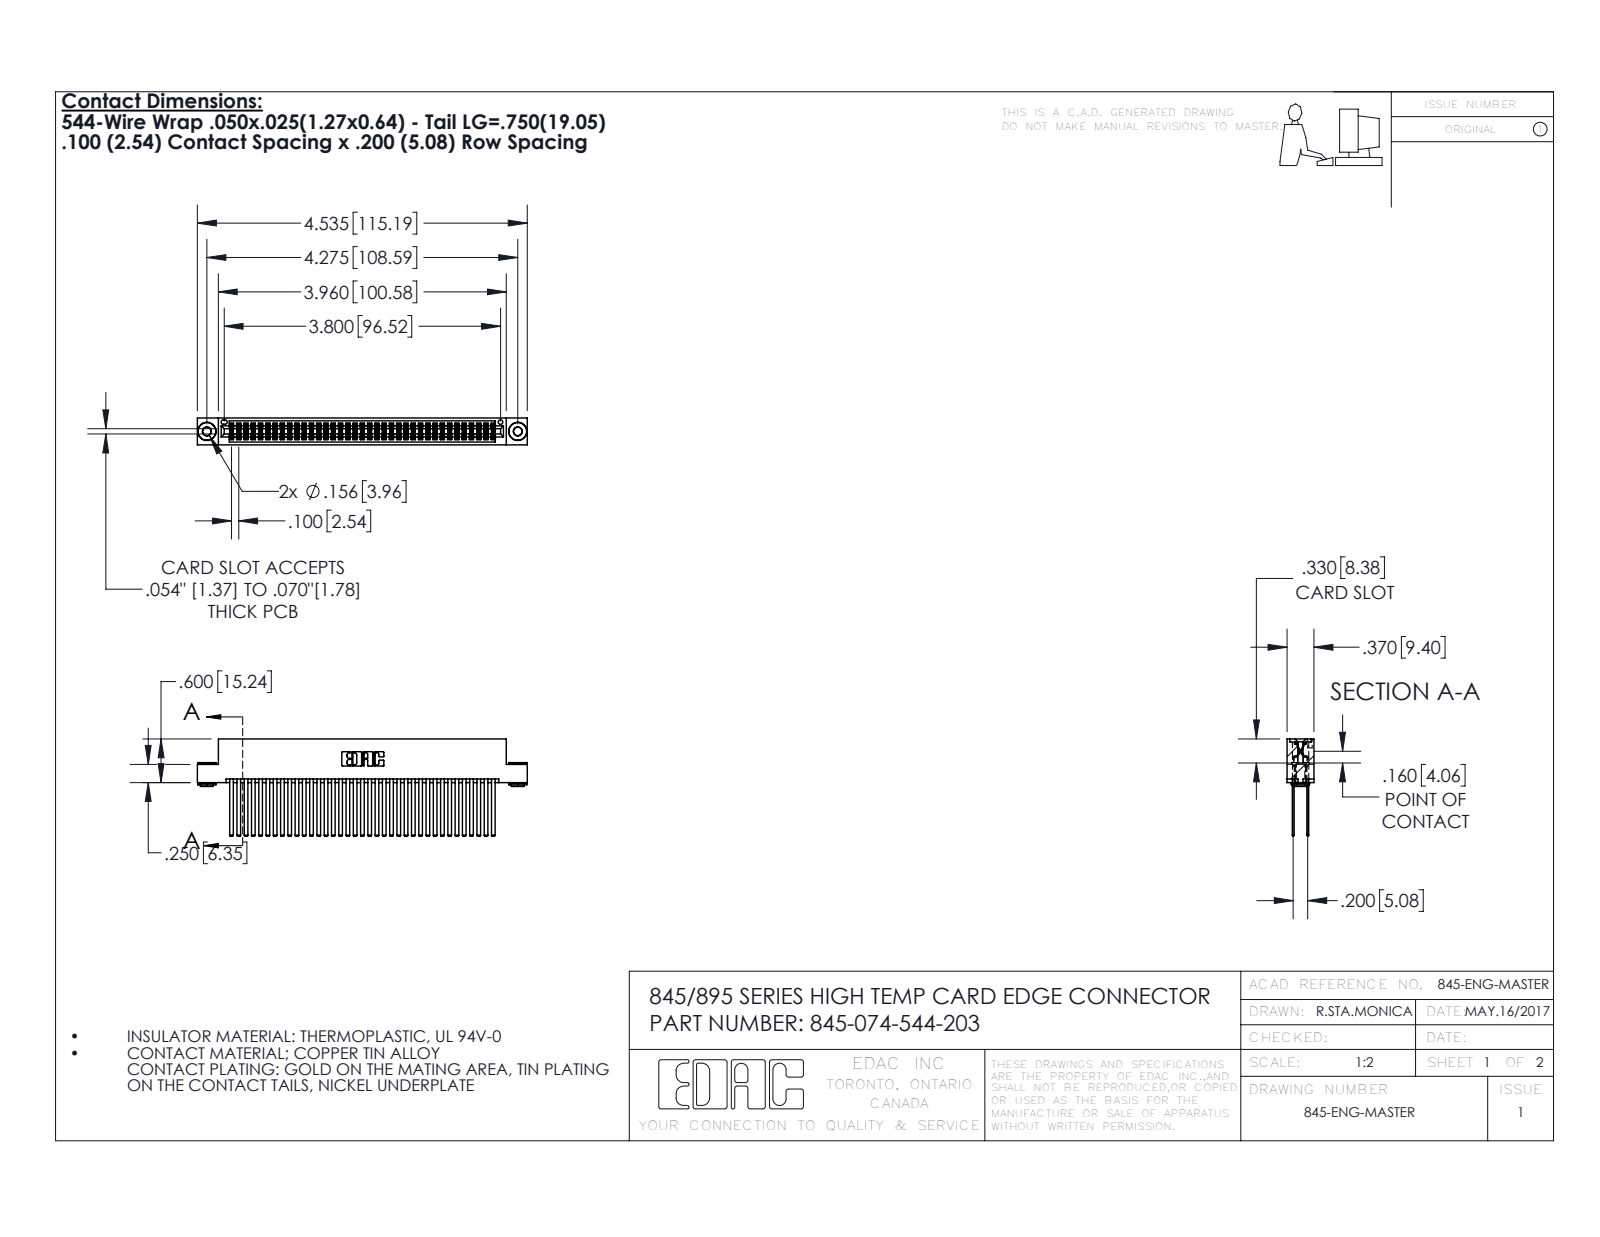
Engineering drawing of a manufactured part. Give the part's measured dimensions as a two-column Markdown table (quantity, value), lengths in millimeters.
| quantity | value |
| --- | --- |
| part name | 345-292-001_345-293-144; 345-250-002_345-250-002-102; 345-074-544-203; 345 Part_Flush Mounting Lugs - 0.156 Dia-TH |
| STEP written by | SolidWorks 2016 (CONFIG_CONTROL_DESIGN) |
| units | millimeters |
| bodies | 77 solids, 3420 faces (2236 planar, 1176 cylindrical, 8 other) |
| overall size | 115.2 × 34 × 9.4 |
| volume | 12 200 mm³ |
| surface area | 21 180 mm² |
| round holes (diameter × count) | 2.9 × 2, 4 × 2, 1.6 × 1 |
| round bosses / shafts (diameter × count) | 6.4 × 2, 4.6 × 2, 3.5 × 2 |
| partial cylindrical surfaces (radius × count) | 0.2 × 111, 0.3 × 22, 0.2 × 6, 0.8 × 6, 0.7 × 3, 0.4 × 2, 0.5 × 2, 0.6 × 2 |
| main face-to-face distances | 5.1, 0.6, 1.8, 2.5, 6.9, 7.6, 5.7, 4.4, 9.4, 1.3 |
| hole center spacings | 6.9, 102.6, 108.6 |
